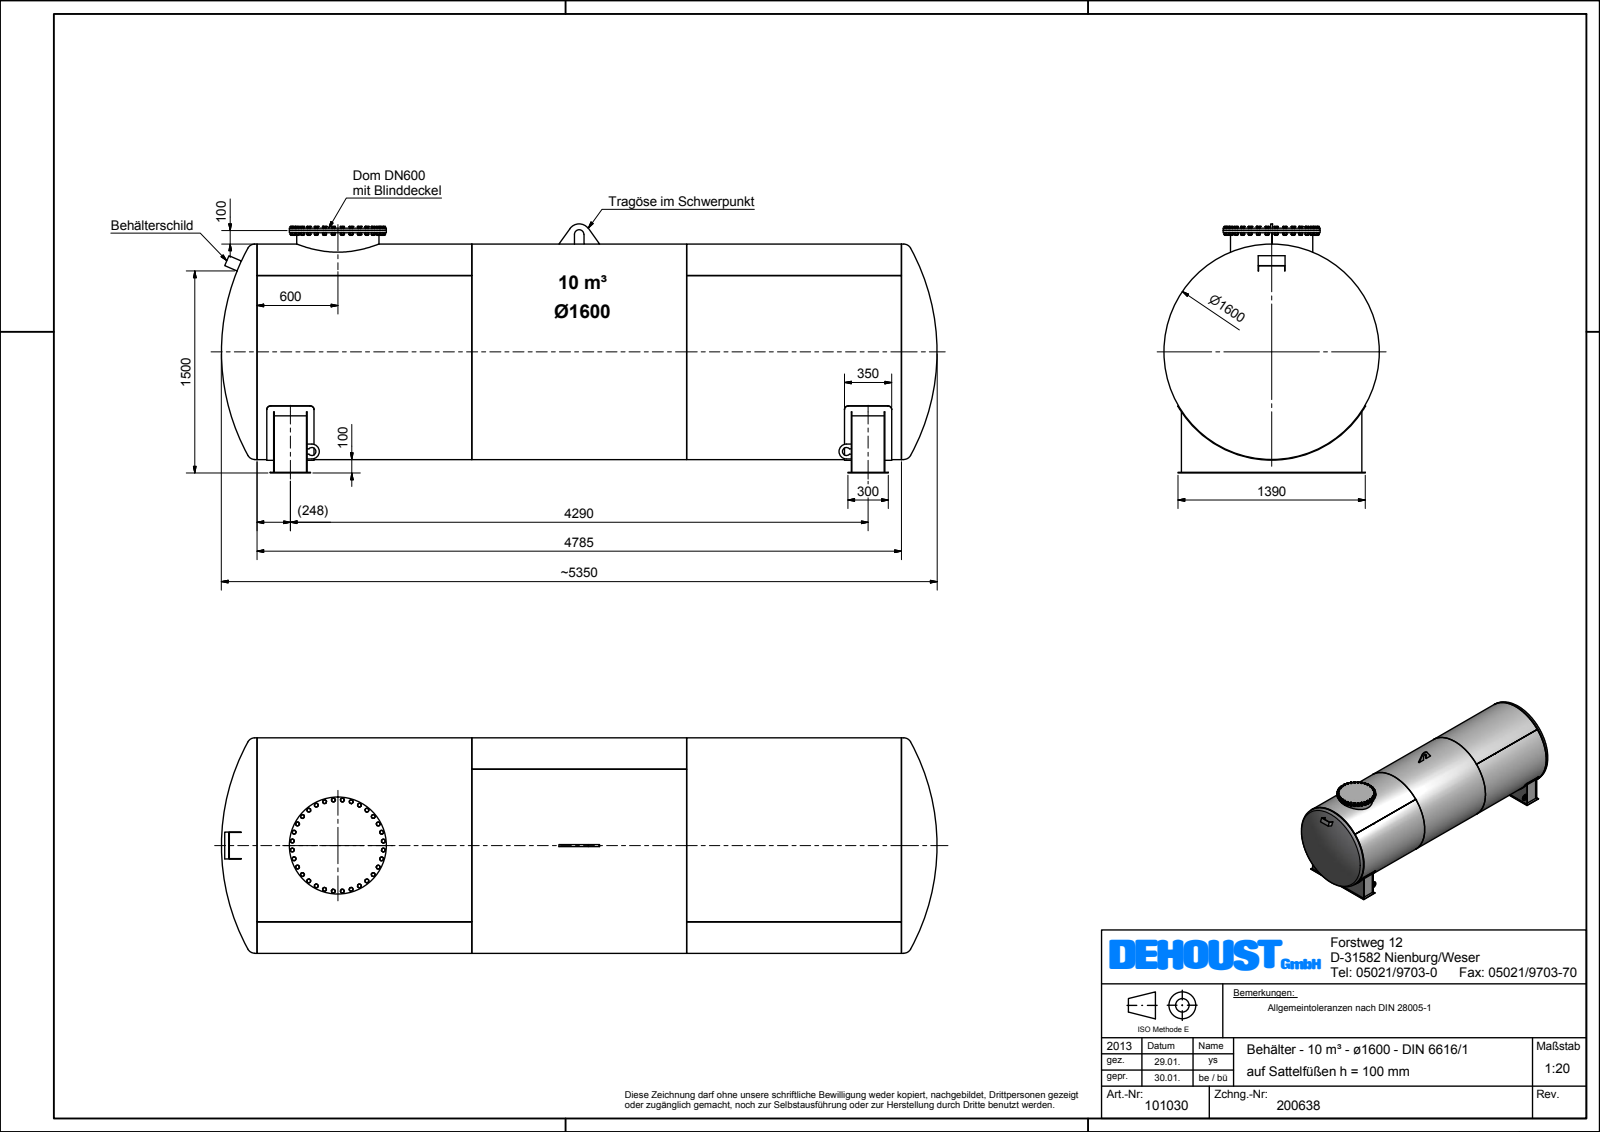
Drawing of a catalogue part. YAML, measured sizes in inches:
part_name: "Beh\\S\\dlter_6616_E_1600_010_100_KV"
step_written_by: "Autodesk Inventor 2012 (AUTOMOTIVE_DESIGN)"
units: inches
bodies: {solids: 3, faces: 1115, planar: 660, cylindrical: 163, other: 292}
overall_size: [209.272, 72.835, 62.992]
volume: 48750
surface_area: 97700
round_holes:
  - {diameter: 23.543, count: 1}
  - {diameter: 62.598, count: 1}
round_bosses_or_shafts:
  - {diameter: 0.976, count: 32}
  - {diameter: 0.709, count: 32}
  - {diameter: 0.656, count: 32}
  - {diameter: 62.992, count: 1}
  - {diameter: 28.346, count: 1}
  - {diameter: 25.984, count: 1}
  - {diameter: 24.016, count: 1}
partial_cylinders:
  - {radius: 1.181, count: 8}
  - {radius: 1.17, count: 2}
  - {radius: 2.165, count: 2}
  - {radius: 1.378, count: 1}
  - {radius: 3.346, count: 1}
  - {radius: 31.693, count: 1}
face_to_face_distances: [0.197, 188.386, 168.898, 9.646, 4.823, 183.563, 14.665, 173.72, 9.843, 5.02]
